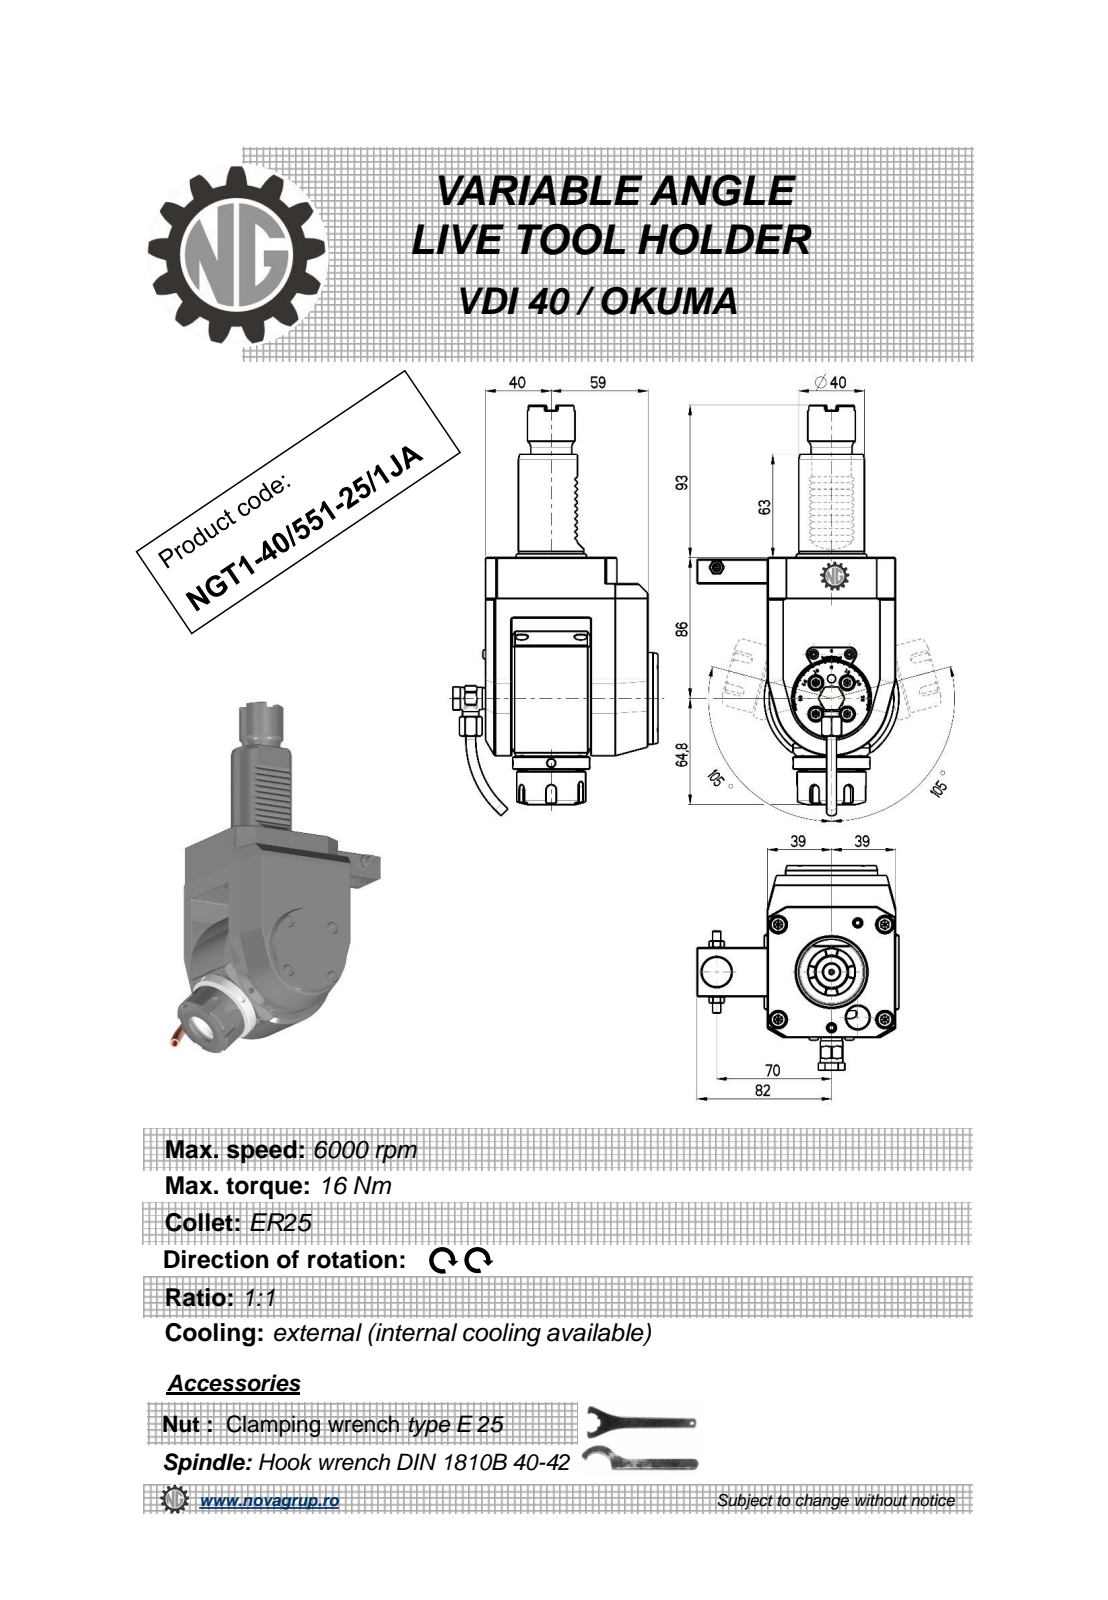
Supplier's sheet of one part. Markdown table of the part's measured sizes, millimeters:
| quantity | value |
| --- | --- |
| part name | NGT1_40_551_25_1JA |
| STEP written by | PRO/ENGINEER BY PARAMETRIC TECHNOLOGY CORPORATION, 2010280 (CONFIG_CONTROL_DESIGN) |
| units | millimeters |
| bodies | 1 solid, 611 faces (252 planar, 138 cylindrical, 221 other) |
| overall size | 250.67 × 124.9 × 123 |
| volume | 941 332 mm³ |
| surface area | 87 917 mm² |
| round holes (diameter × count) | 4 × 3, 5 × 2, 3 × 1, 4.2 × 1, 6.2 × 1, 9 × 1, 9.5 × 1, 10 × 1, 11 × 1, 18 × 1, 20.3 × 1 |
| round bosses / shafts (diameter × count) | 6 × 2, 5.7 × 2, 82 × 1, 56 × 1, 47 × 1, 42 × 1, 40 × 1, 36 × 1 |
| partial cylindrical surfaces (radius × count) | 0.26 × 12, 0.3 × 10, 3 × 5, 0.5 × 4, 10 × 3, 1 × 2, 7.7 × 1, 35 × 1 |
| main face-to-face distances | 16, 37, 64, 99, 78, 6, 105, 1, 21, 25 |
| hole center spacings | 0.4, 39.45, 49, 49.4, 70, 85.45, 85.68, 106.3 |
